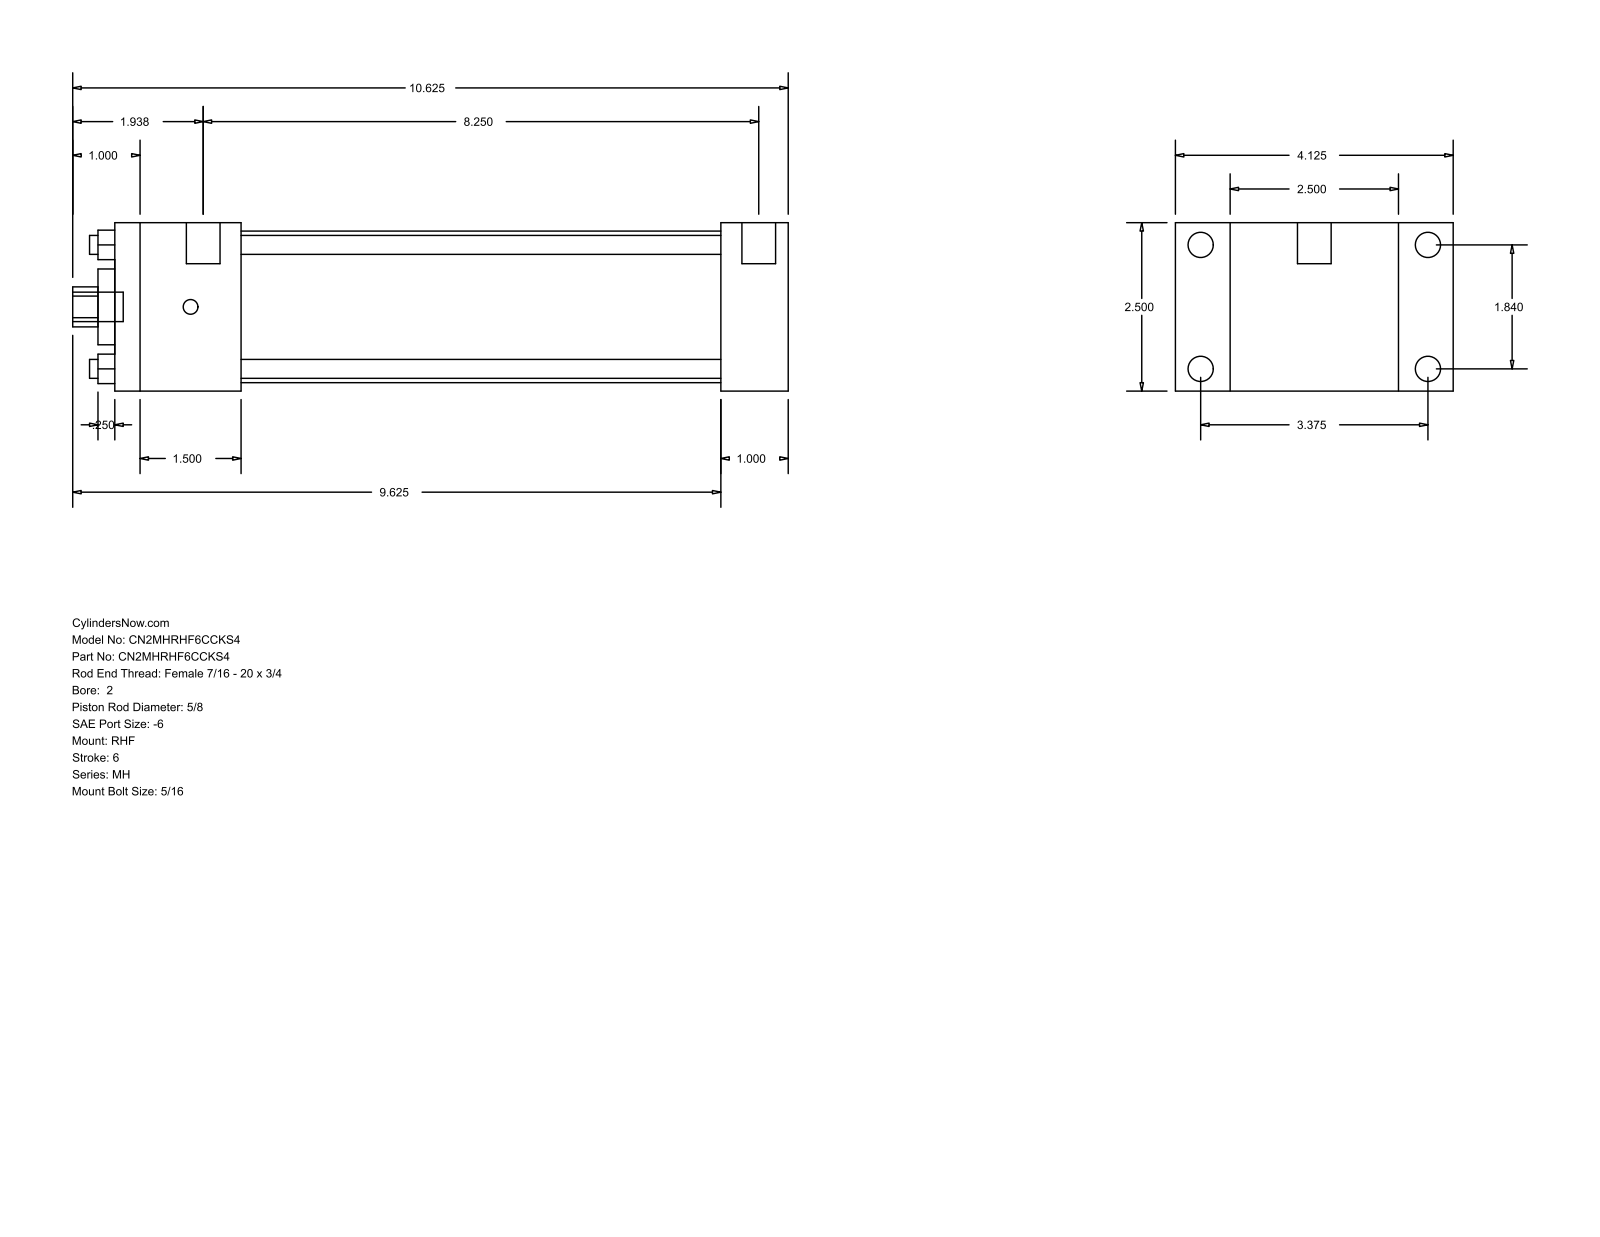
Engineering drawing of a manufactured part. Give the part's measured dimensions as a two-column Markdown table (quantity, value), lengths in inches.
| quantity | value |
| --- | --- |
| part name | MH_RHF__0200_0.625 |
| STEP written by | GSSL Pune (CONFIG_CONTROL_DESIGN) |
| units | inches |
| bodies | 0 solids, 88 faces (60 planar, 28 cylindrical, 0 other) |
| overall size | 10.625 × 4.125 × 2.5 |
| round holes (diameter × count) | 0.281 × 4, 0.625 × 1, 1.125 × 1, 2.25 × 1 |
| round bosses / shafts (diameter × count) | 0.375 × 4, 0.219 × 4, 0.5 × 2, 0.437 × 1 |
| partial cylindrical surfaces (radius × count) | 0.297 × 1 |
| main face-to-face distances | 2.5, 1, 0.813, 3.313, 9, 10, 4.125, 1.875, 7.125, 8.125 |
| hole center spacings | 1.301, 1.84, 2.602 |
